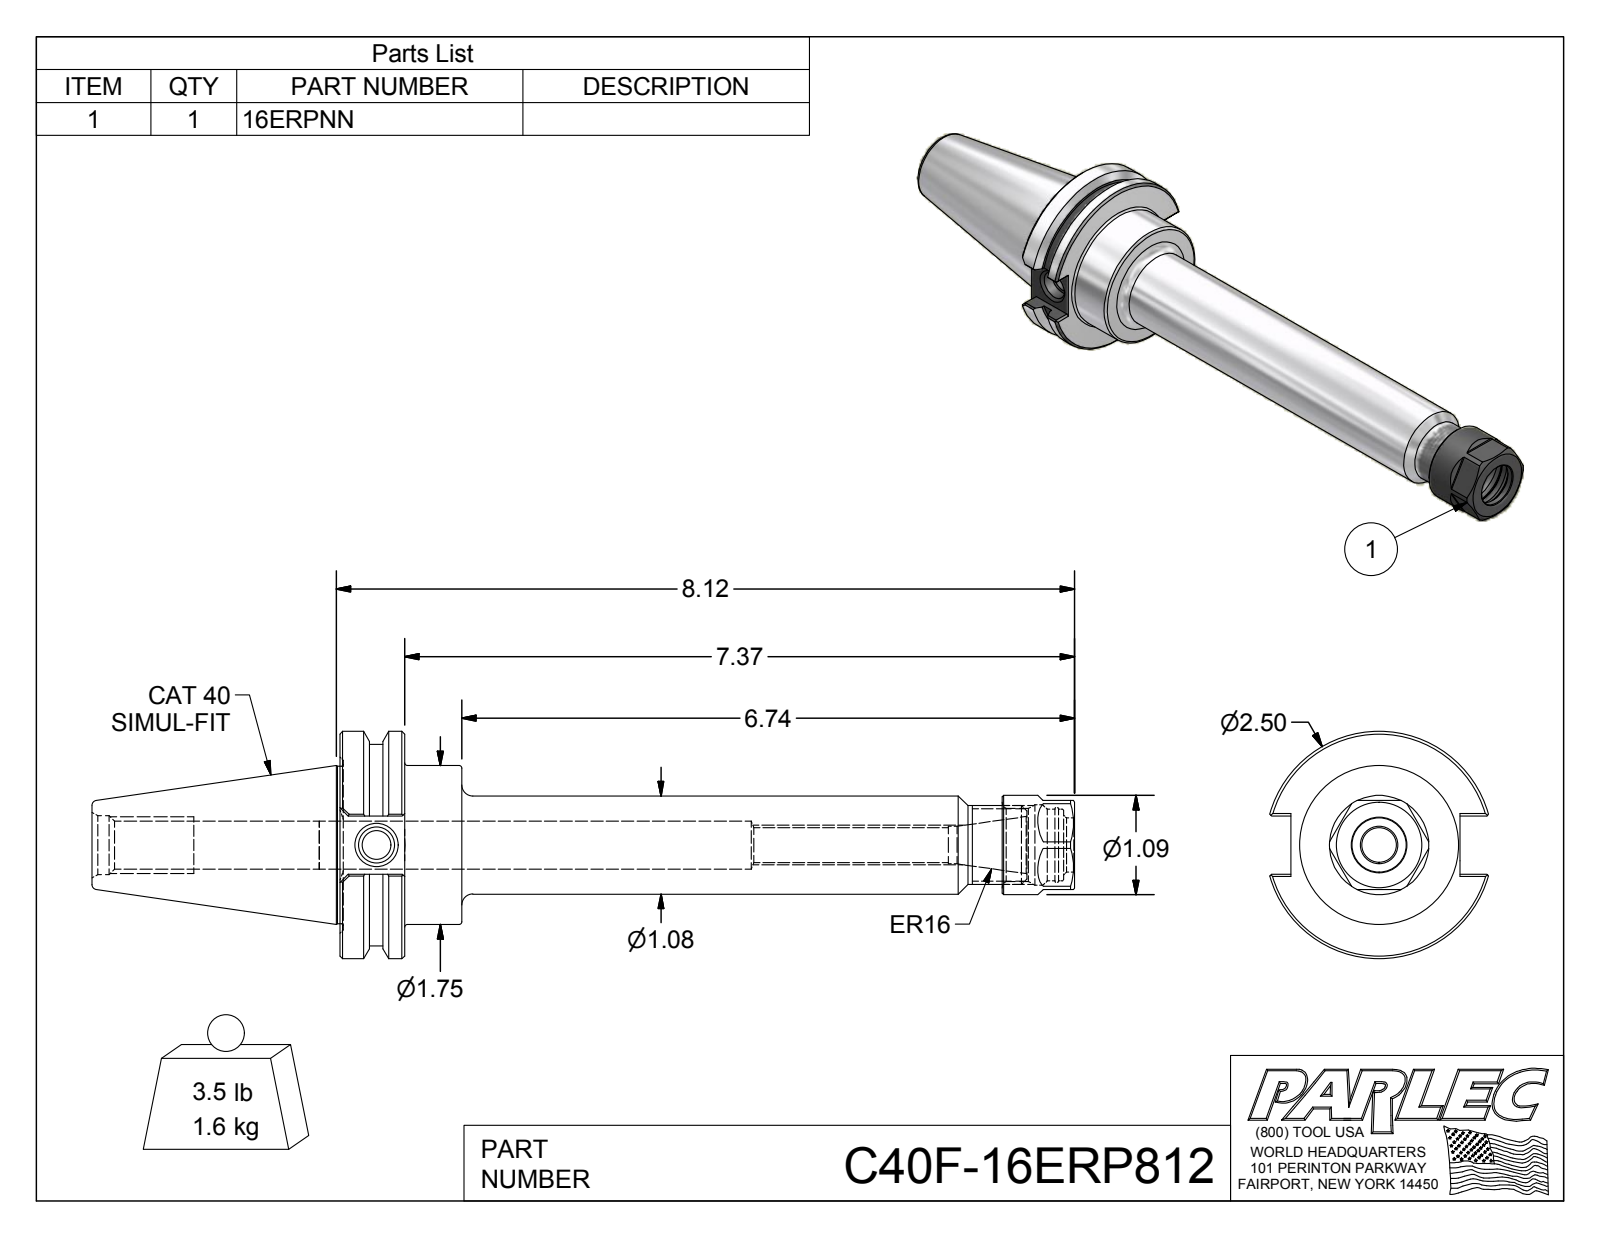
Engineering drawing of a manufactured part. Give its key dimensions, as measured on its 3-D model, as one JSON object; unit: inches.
{"part_name": "C40F-16ERP812; C40F-16ER8-1; 16ERPNN", "step_written_by": "Autodesk Inventor 2012 (AUTOMOTIVE_DESIGN)", "units": "inches", "bodies": {"solids": 2, "faces": 118, "planar": 49, "cylindrical": 29, "other": 40}, "overall_size": [10.808, 2.5, 2.406], "volume_in3": 12.32, "surface_area_in2": 71.47, "round_holes": [[0.315, 1], [0.383, 1], [0.399, 1], [0.413, 1], [0.527, 1], [0.527, 1], [0.596, 1], [0.648, 1], [0.789, 1], [0.802, 1], [0.883, 1]], "round_bosses_or_shafts": [[2.5, 1], [2.215, 1], [1.75, 1], [1.73, 1], [1.092, 1], [1.08, 1], [0.866, 1]], "partial_cylinders_radius": [[0.02, 6]], "face_to_face_distances": [0.711, 1.341, 0.63, 0.98, 8.081, 7.37, 6.74, 0.17, 0.81, 1.86]}
